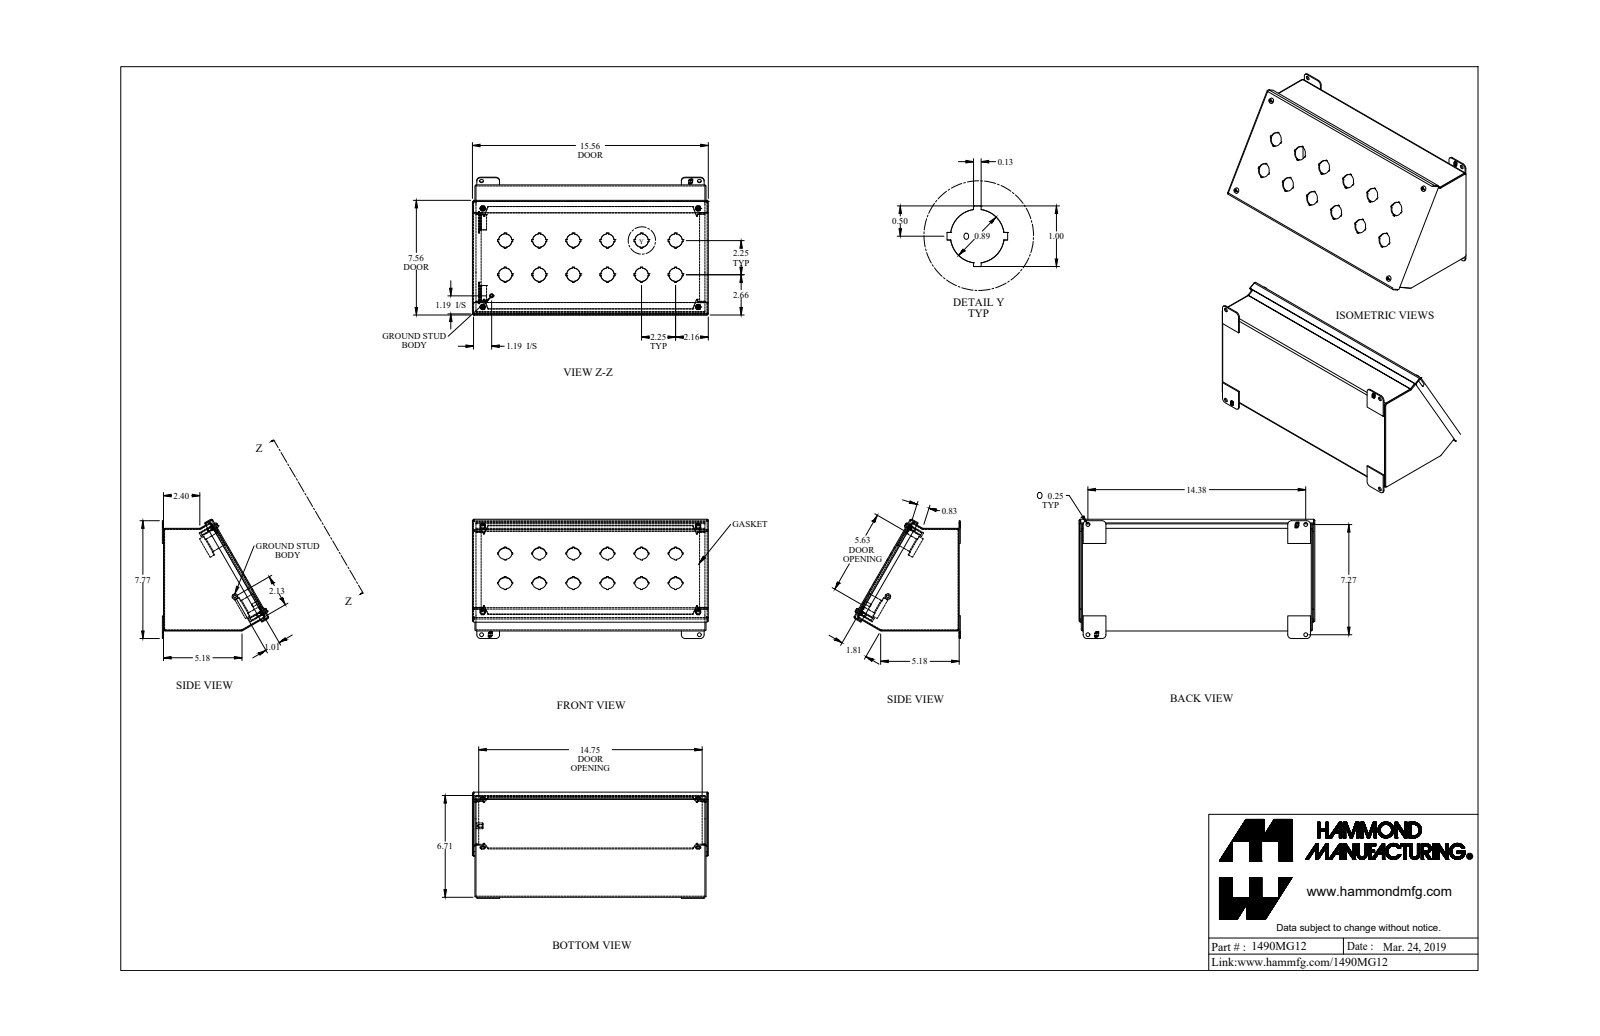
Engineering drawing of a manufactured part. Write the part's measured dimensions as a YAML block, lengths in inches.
part_name: "1490MG12_Default"
step_written_by: "SolidWorks 2019 (CONFIG_CONTROL_DESIGN)"
units: inches
bodies: {solids: 26, faces: 886, planar: 627, cylindrical: 221, other: 38}
overall_size: [15.562, 7.891, 7.053]
volume: 34.36
surface_area: 977.5
round_holes:
  - {diameter: 0.25, count: 8}
  - {diameter: 0.875, count: 8}
  - {diameter: 0.159, count: 4}
  - {diameter: 0.875, count: 4}
  - {diameter: 0.12, count: 1}
  - {diameter: 0.136, count: 1}
  - {diameter: 0.156, count: 1}
round_bosses_or_shafts:
  - {diameter: 0.39, count: 4}
  - {diameter: 0.275, count: 4}
  - {diameter: 0.19, count: 4}
  - {diameter: 0.148, count: 4}
  - {diameter: 0.375, count: 1}
  - {diameter: 0.29, count: 1}
partial_cylinders:
  - {radius: 0.108, count: 18}
  - {radius: 0.036, count: 12}
  - {radius: 0.029, count: 8}
  - {radius: 0.086, count: 8}
  - {radius: 0.25, count: 8}
  - {radius: 0.125, count: 4}
  - {radius: 0.16, count: 4}
  - {radius: 0.171, count: 4}
face_to_face_distances: [0.072, 6.698, 15.178, 15.106, 6.77, 6.626, 15.25, 7.334, 0.072, 0.156]
hole_center_spacings: [2.25, 3.182, 4.5, 5.031, 6.75, 7.115, 7.409, 9.32]
